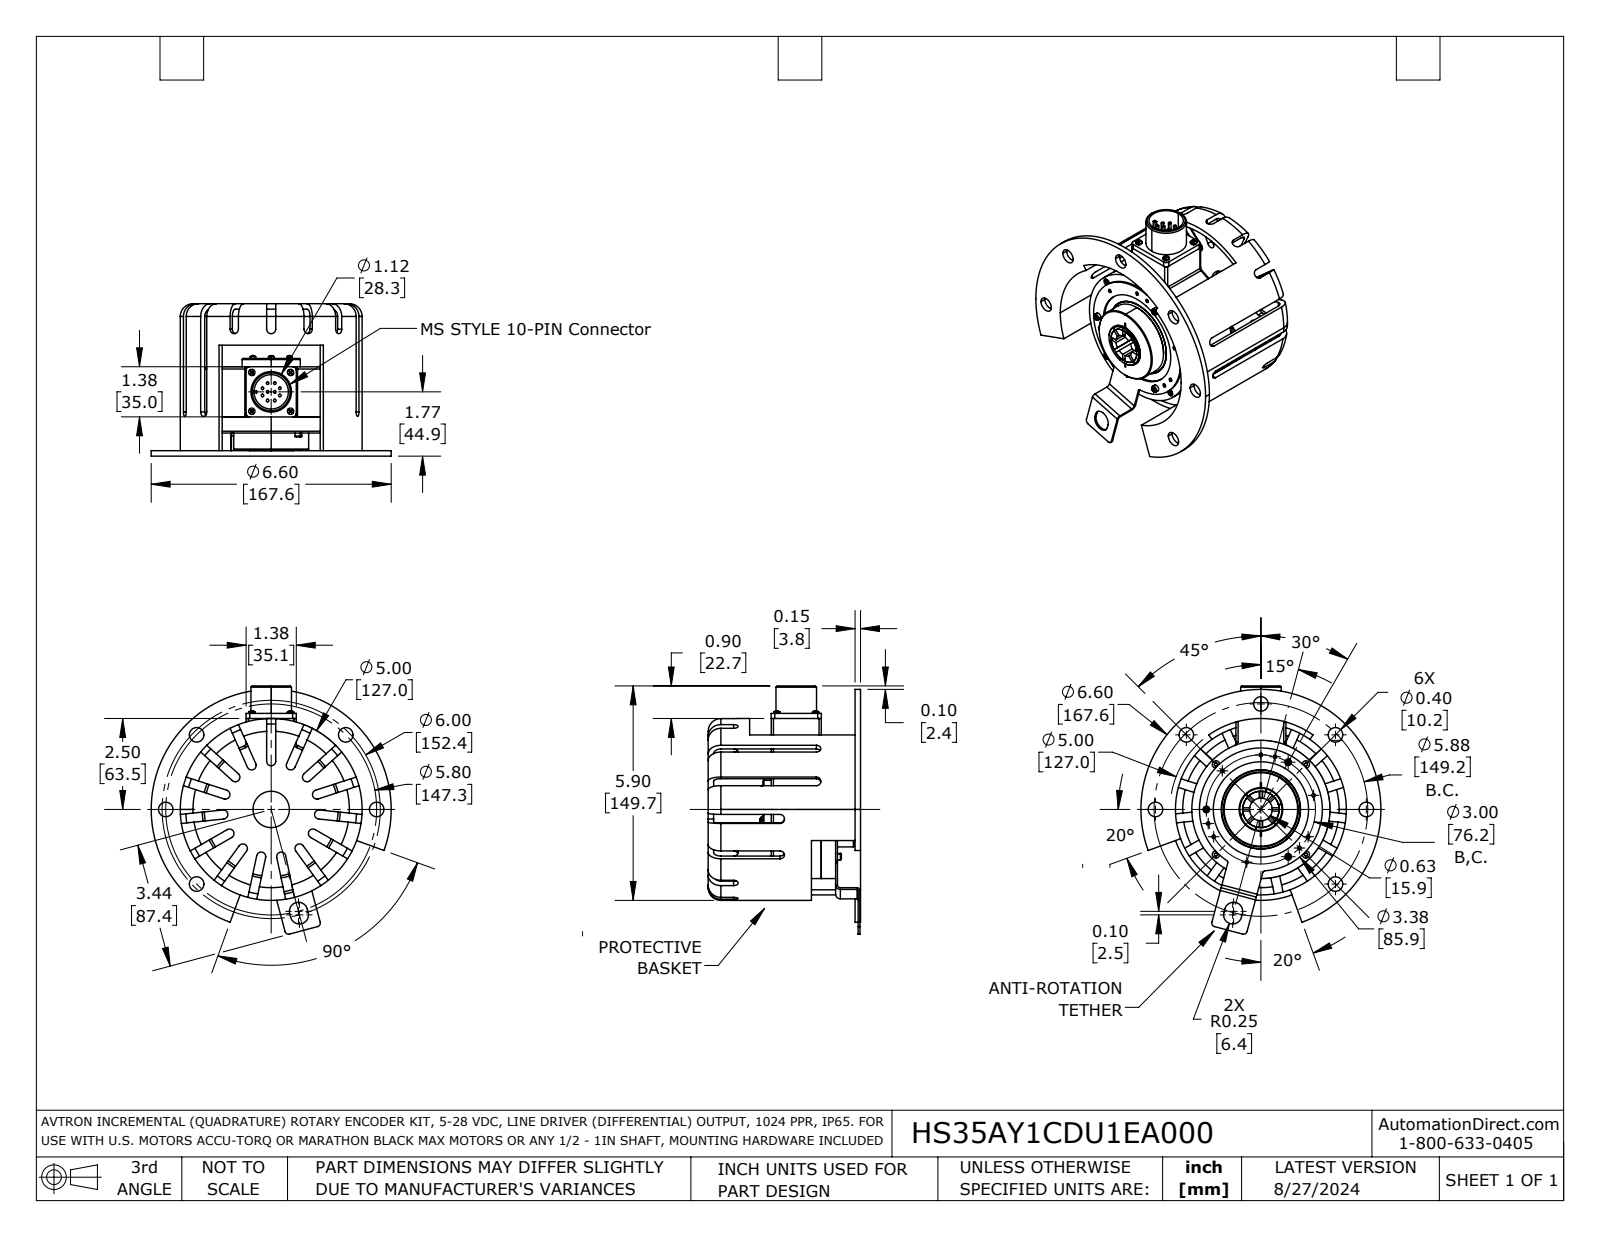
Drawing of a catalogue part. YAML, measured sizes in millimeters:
part_name: "HS35AY1CDU1EA000"
step_written_by: "SolidWorks 2021 (AUTOMOTIVE_DESIGN)"
units: millimeters
bodies: {solids: 18, faces: 724, planar: 327, cylindrical: 289, other: 108}
overall_size: [173.4, 167.6, 106.4]
volume: 536000
surface_area: 175100
round_holes:
  - {diameter: 2.5, count: 12}
  - {diameter: 10.2, count: 6}
  - {diameter: 3, count: 4}
  - {diameter: 5.1, count: 4}
  - {diameter: 3.5, count: 3}
  - {diameter: 15.9, count: 1}
  - {diameter: 24, count: 1}
  - {diameter: 25.4, count: 1}
  - {diameter: 55.4, count: 1}
  - {diameter: 66.5, count: 1}
  - {diameter: 119.4, count: 1}
round_bosses_or_shafts:
  - {diameter: 1.8, count: 8}
  - {diameter: 4.4, count: 4}
  - {diameter: 4.6, count: 3}
  - {diameter: 3.8, count: 3}
  - {diameter: 2.9, count: 3}
  - {diameter: 1.8, count: 2}
  - {diameter: 127, count: 1}
  - {diameter: 96.5, count: 1}
partial_cylinders:
  - {radius: 3.2, count: 30}
  - {radius: 1.5, count: 6}
  - {radius: 2.5, count: 6}
  - {radius: 1.2, count: 4}
  - {radius: 1.3, count: 2}
  - {radius: 2, count: 2}
  - {radius: 6.4, count: 2}
  - {radius: 0.8, count: 1}
face_to_face_distances: [3.8, 102.6, 10, 45, 34.9, 62.4, 27.4, 17.4, 44.1, 79]
hole_center_spacings: [38.1, 66, 98.4, 29.2, 38.2, 46.4, 52.6, 63.8]
